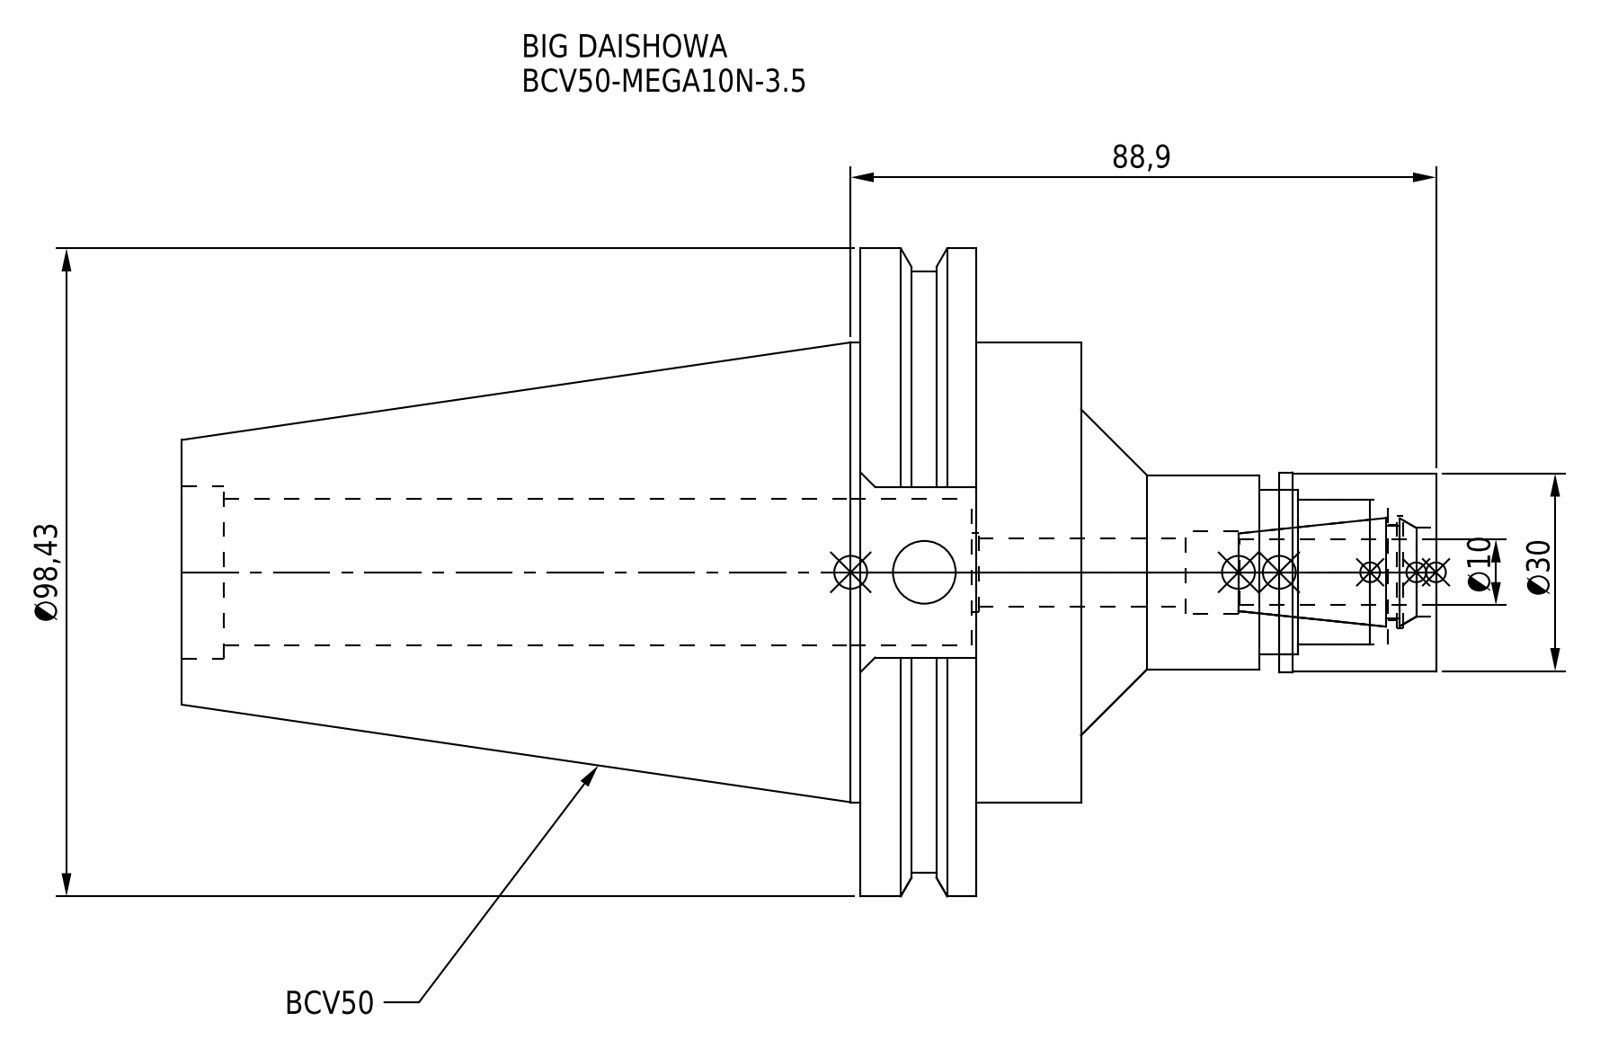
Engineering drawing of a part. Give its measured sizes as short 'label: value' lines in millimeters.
name: BCV50MN10035-100_ASM.stp; BCV50-MEGA10N-3_5_1.stp; BCV50-MEGA10N-3_5-100-FreeParts; BCV50-MEGA10N-3_5-100.stp (+3 more)
written by: SolidWorks 2019 (CONFIG_CONTROL_DESIGN)
unit: mm
bodies: 2 solids, 91 faces (33 planar, 44 cylindrical, 14 other)
size: 190.5 × 98.42 × 94.95
volume: 417 881 mm³; area: 58 897 mm²
holes: 1× ⌀9.53, 1× ⌀10.4, 1× ⌀12, 1× ⌀12.5, 1× ⌀13.5, 1× ⌀14.5, 1× ⌀17, 1× ⌀22, 1× ⌀22.3, 1× ⌀25, 1× ⌀26.23
bosses: 1× ⌀98.42, 1× ⌀91.29, 1× ⌀69.85, 1× ⌀30.3, 1× ⌀30, 1× ⌀29.5
face distances: 17.55, 15.95, 33.5, 136.6, 120.65, 103.1, 69.85, 53.9, 87.4, 190.5
